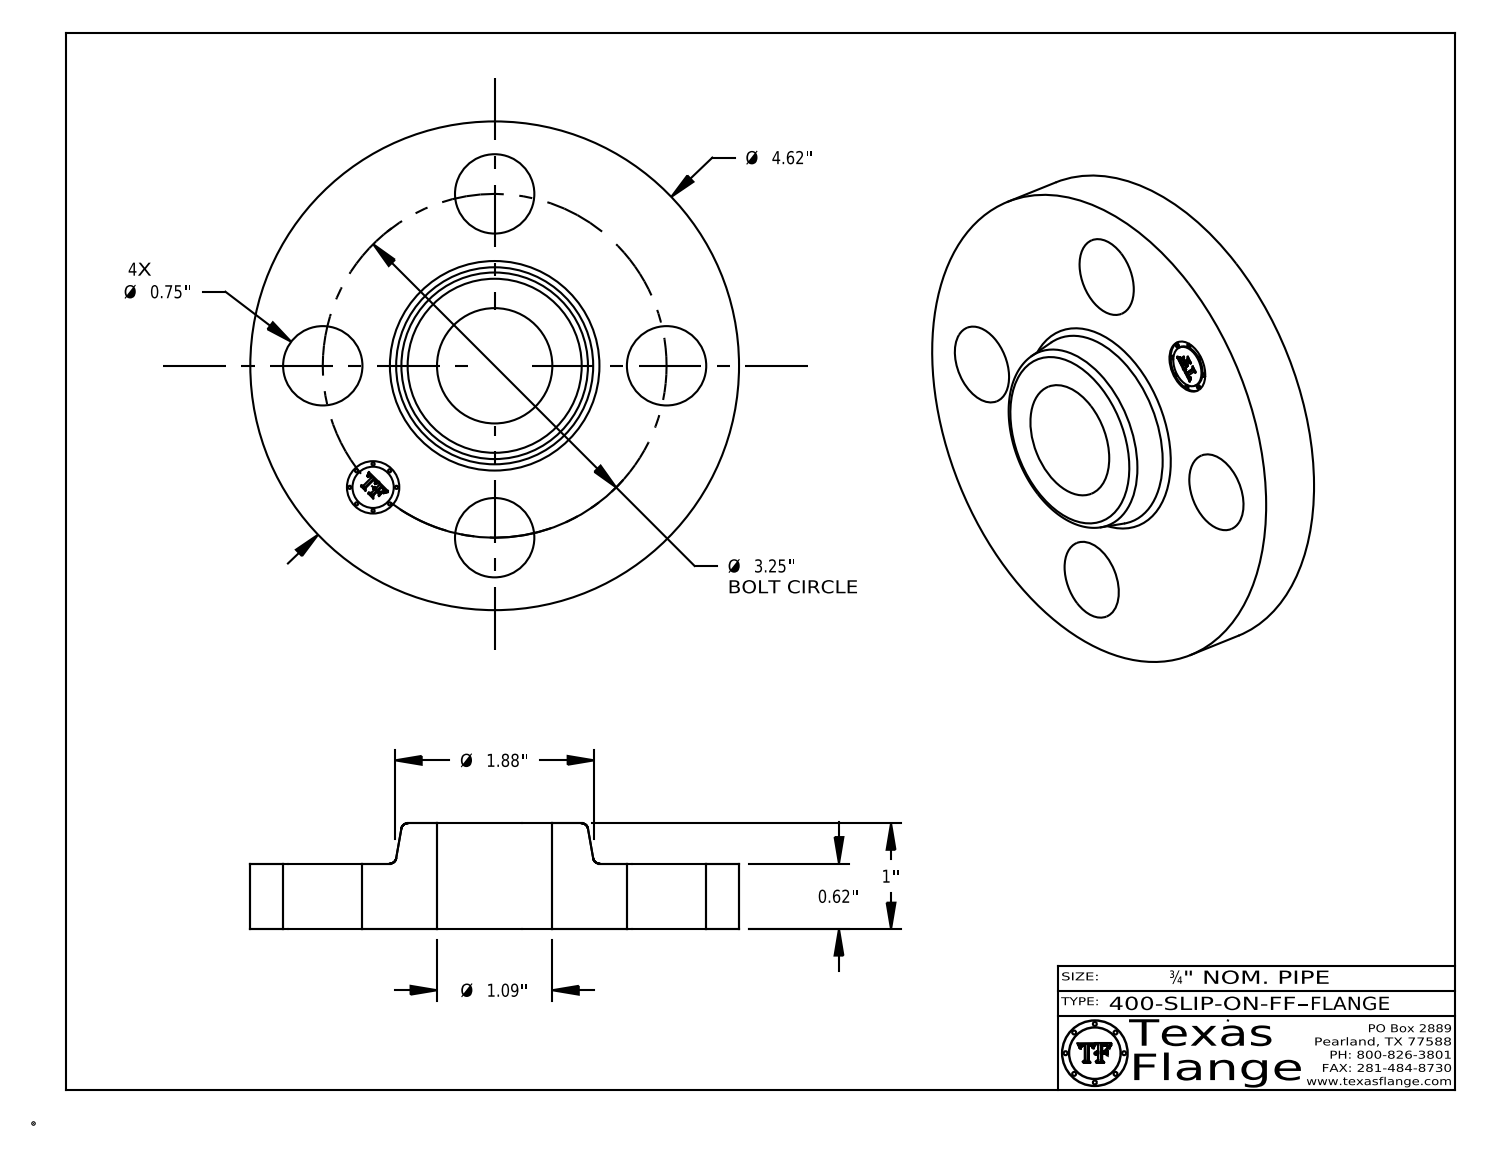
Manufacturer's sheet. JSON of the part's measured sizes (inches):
{"part_name": "400-SLIP-ON-FF", "step_written_by": "CATIA V5 STEP AP214 (AUTOMOTIVE_DESIGN)", "units": "inches", "bodies": {"solids": 1, "faces": 406, "planar": 368, "cylindrical": 32, "other": 6}, "overall_size": [4.62, 4.62, 1], "volume_in3": 9.345, "surface_area_in2": 48.11, "round_holes": [[0.75, 4], [0.495, 1], [1.09, 1]], "round_bosses_or_shafts": [[0.03, 8], [4.62, 1], [0.39, 1]], "face_to_face_distances": [0.62, 1, 0.38, 0.605, 0.015, 0.395, 0.148, 0.144, 0.027, 0.096], "hole_center_spacings": [1.625, 2.298, 1.244, 3.003, 3.25]}
